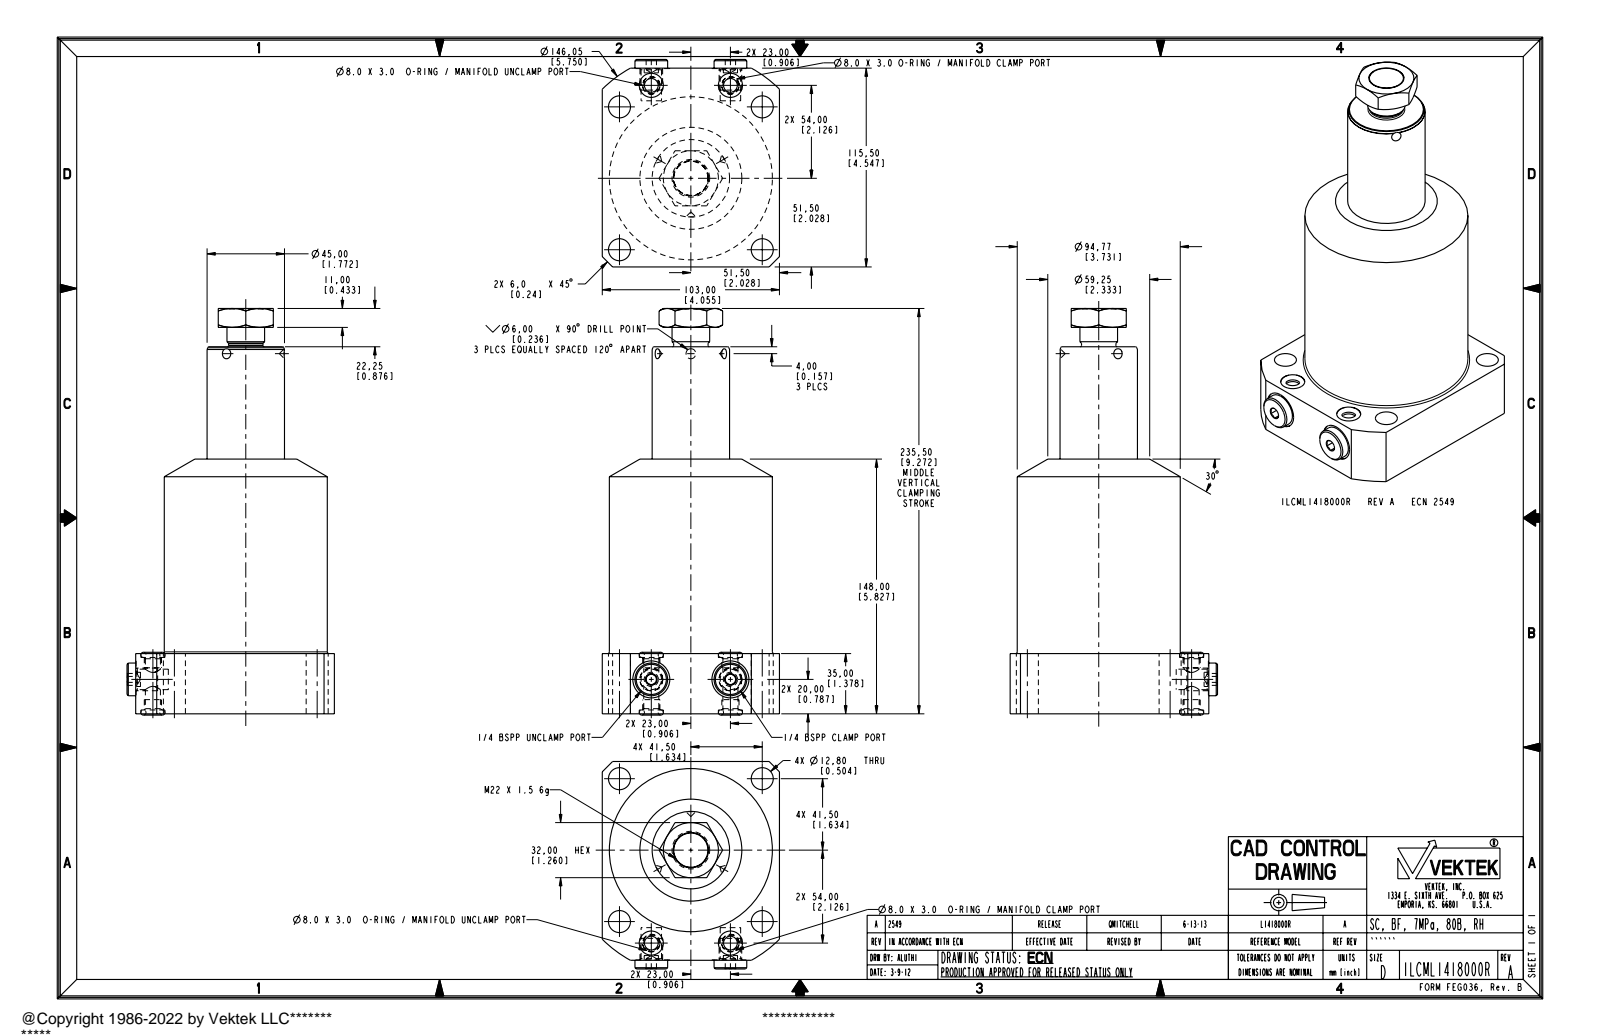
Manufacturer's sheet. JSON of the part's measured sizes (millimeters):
{"part_name": "ILCML1418000R", "step_written_by": "PRO/ENGINEER BY PARAMETRIC TECHNOLOGY CORPORATION, 2007460 (AUTOMOTIVE_DESIGN_CC2)", "units": "millimeters", "bodies": {"solids": 5, "faces": 212, "planar": 63, "cylindrical": 64, "other": 85}, "overall_size": [236.25, 120.55, 103], "volume_mm3": 1277000, "surface_area_mm2": 92856, "round_holes": [[12.8, 4], [8.75, 2], [11.89, 2], [14, 2], [21.5, 2], [20.5, 1]], "round_bosses_or_shafts": [[19, 2], [13.16, 2], [10, 2], [8.25, 2], [94.77, 1], [45, 1], [21.87, 1], [20, 1]], "partial_cylinders_radius": [[73.03, 1]], "face_to_face_distances": [35, 103, 115.5, 148, 113, 213.25, 178.25, 65.25, 235.5, 200.5], "hole_center_spacings": [58.69, 83, 22.33, 46, 65.7, 97.28, 115.24, 117.38]}
